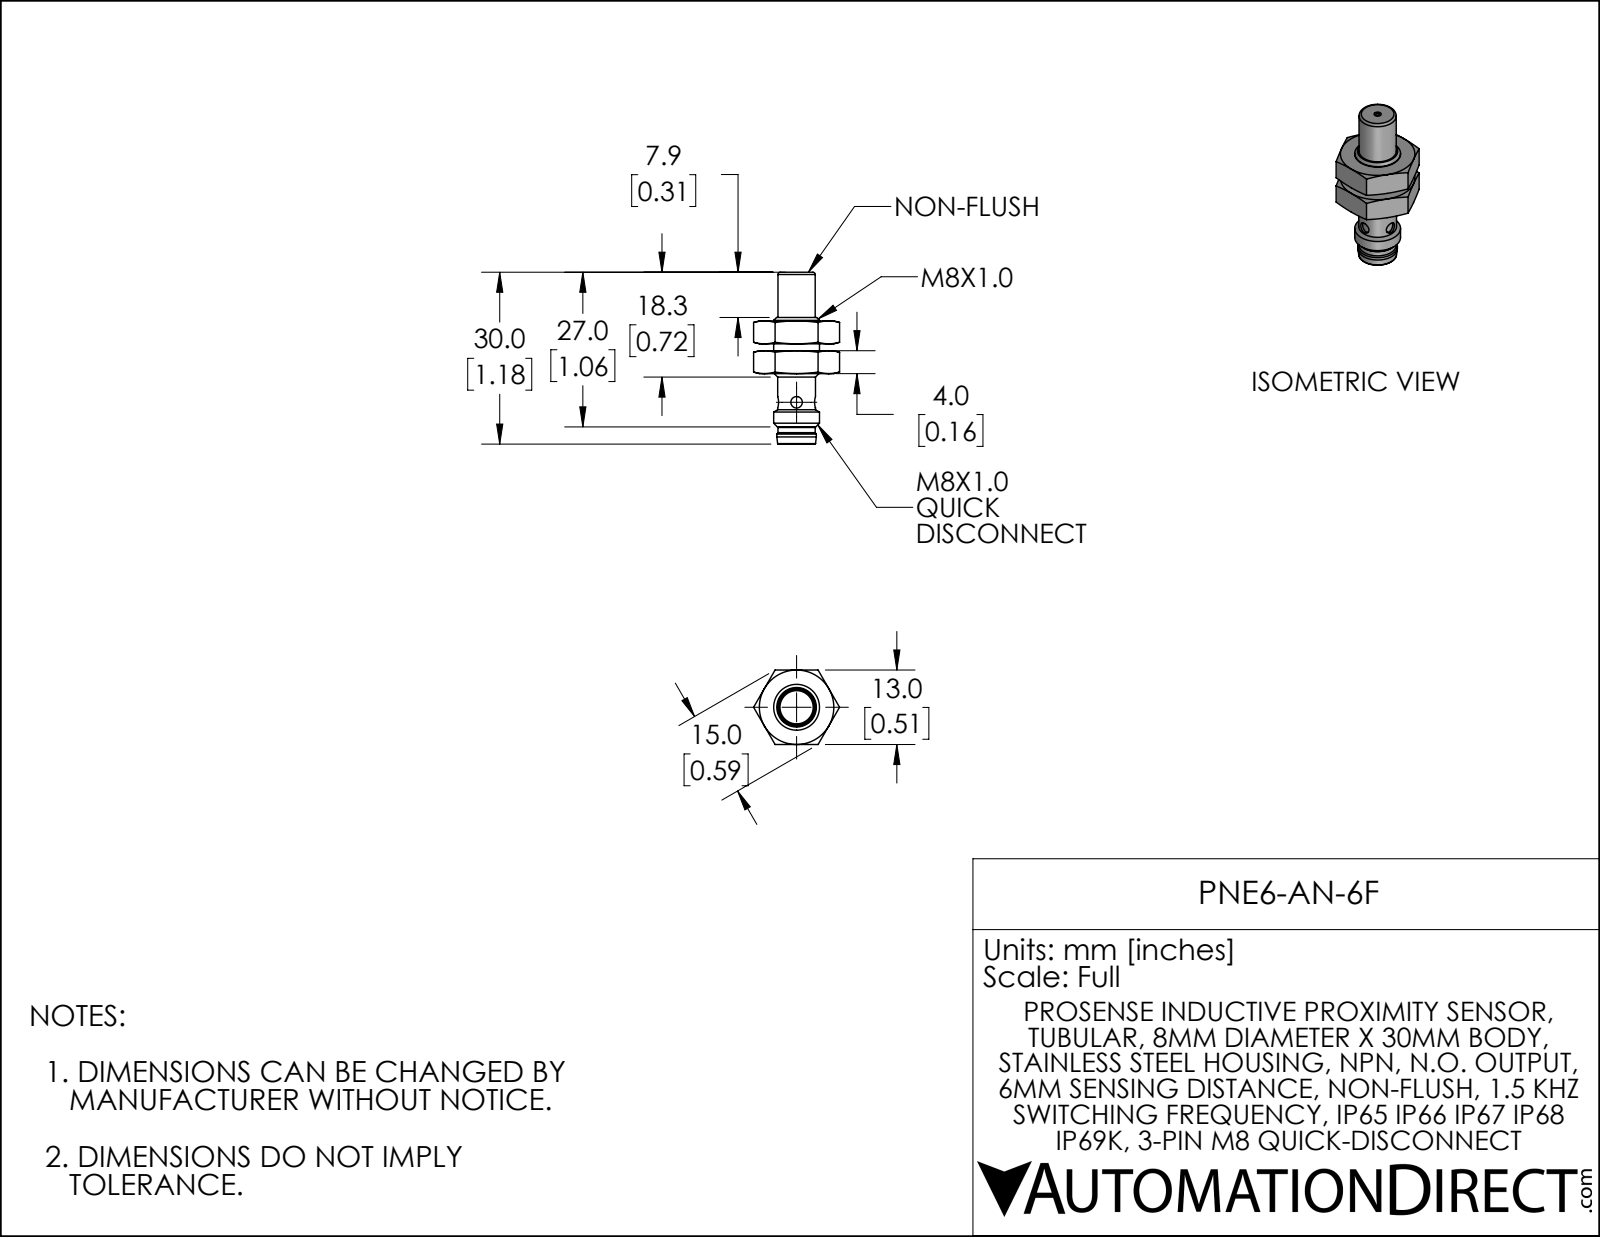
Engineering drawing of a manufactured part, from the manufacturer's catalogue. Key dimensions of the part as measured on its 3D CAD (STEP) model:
Part name (STEP PRODUCT): PNE6-AN-6F
STEP written by: SolidWorks 2019 (CONFIG_CONTROL_DESIGN)
Units: inches
Bodies: 3 solids, 79 faces (22 planar, 18 cylindrical, 39 other)
Overall size (bounding box): 1.181 × 0.591 × 0.512
Volume: 0.118 in³ · Surface area: 2.798 in²
Round holes (diameter × count): ⌀0.079 ×2, ⌀0.272 ×1
Round bosses / shafts (diameter × count): ⌀0.315 ×1, ⌀0.272 ×1, ⌀0.26 ×1, ⌀0.256 ×1, ⌀0.25 ×1, ⌀0.228 ×1
Main face-to-face distances: 0.512, 0.157, 0.315, 0.325, 0.482, 0.64, 0.982, 0.657, 0.5, 0.343
